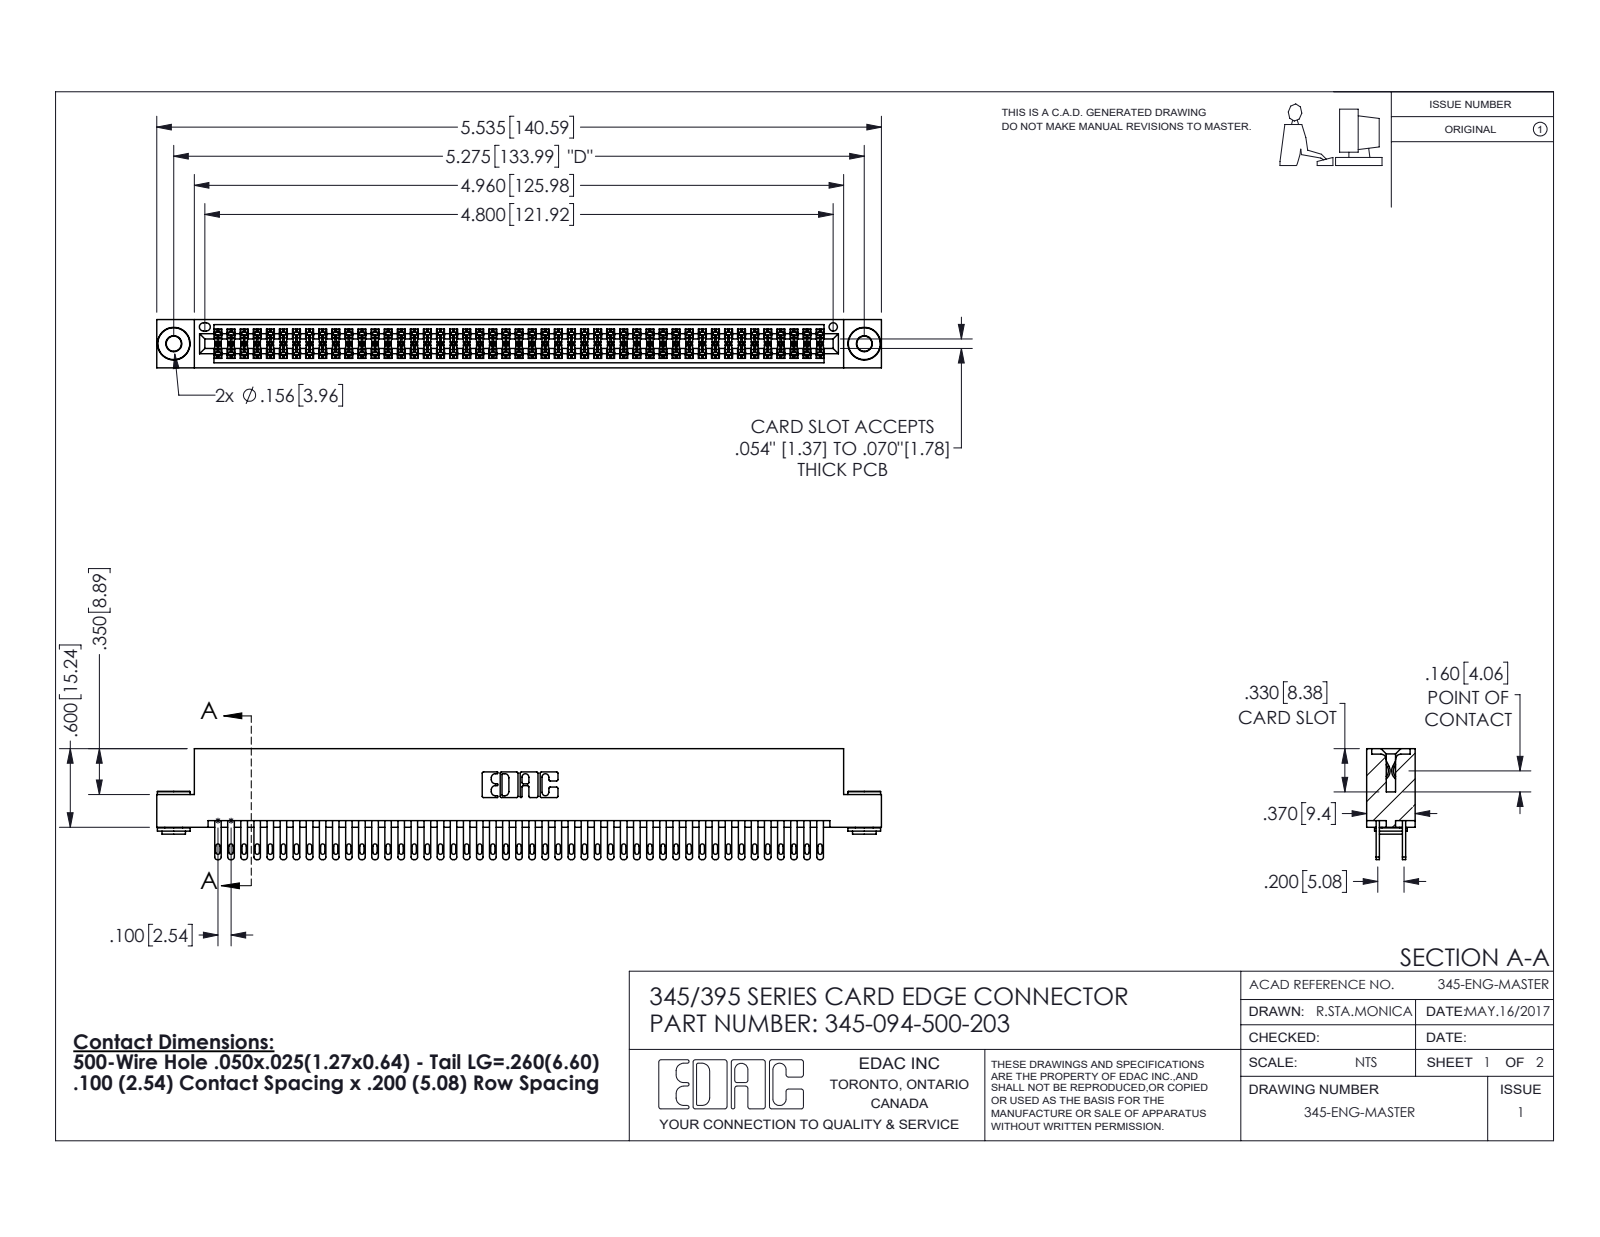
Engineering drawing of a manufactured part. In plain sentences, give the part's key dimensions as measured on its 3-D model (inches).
The part is named "345-094-500-203; 345-292-001_345-293-100; 345-250-002_345-250-002-102; 345 Part_Flush Mounting Lugs - 0.156 Dia-TH". Its 3-D file was written by "SolidWorks 2016 (CONFIG_CONTROL_DESIGN)". It is 97 solids with 4488 faces: 2628 planar, 1852 cylindrical and 8 other. Overall it measures 5.535 by 0.847 by 0.37 inches. Its volume is 0.855 cubic inches and its surface area 34.05 square inches. Round holes: 2 of diameter 0.116, 2 of diameter 0.156, 1 of diameter 0.064. Round bosses or shafts: 2 of diameter 0.25, 2 of diameter 0.18, 2 of diameter 0.136. Partial cylindrical surfaces (rounded edges, fillets, slot ends): 141 of radius 0.006, 94 of radius 0.016, 94 of radius 0.02, 22 of radius 0.01, 6 of radius 0.007, 6 of radius 0.031, 3 of radius 0.026, 2 of radius 0.014. The main face-to-face distances are 0.072, 0.298, 0.2, 0.025, 0.098, 0.272, 0.37, 0.225, 0.175, 0.149. The hole center spacings are 0.27, 5.039, 5.275.
